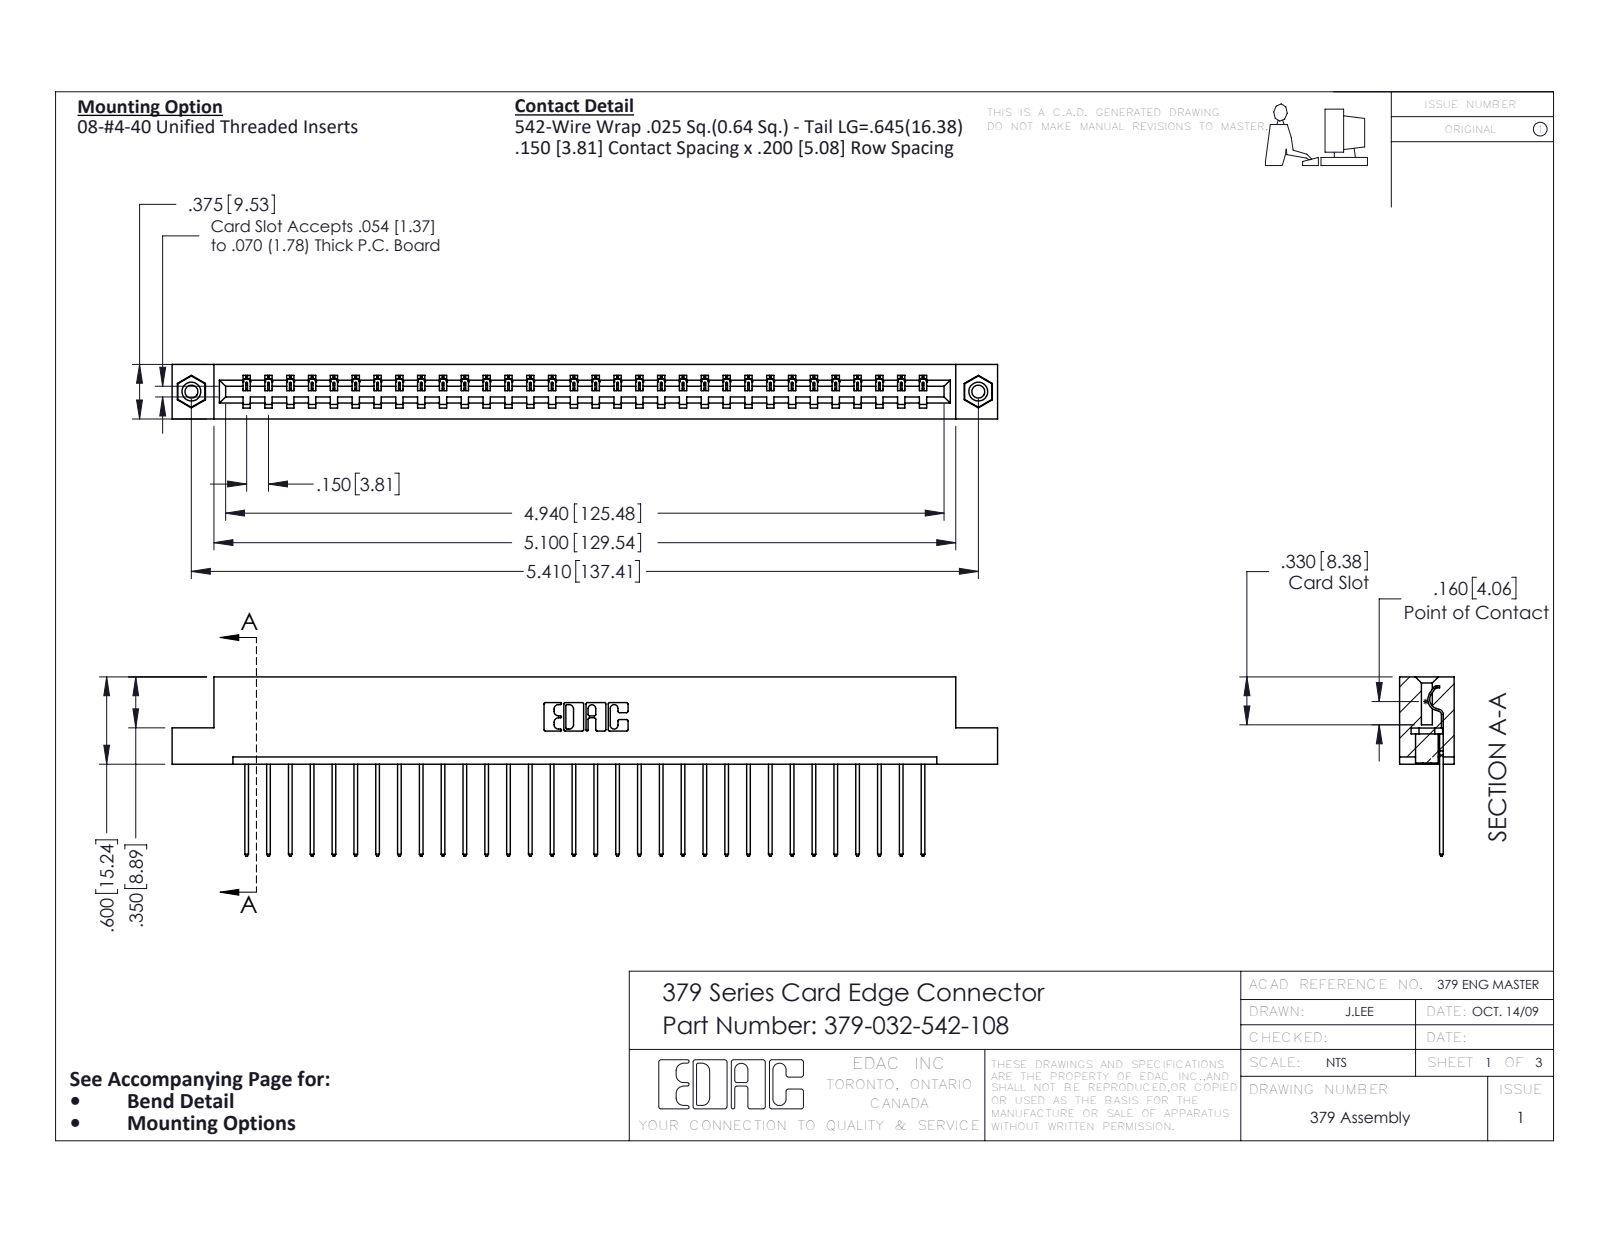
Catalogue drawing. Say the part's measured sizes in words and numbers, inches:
The part is named "345-292-001_345-293-142; 379-032-542-108; 345-250-001_345-250-003-102; 379 Part_Flush - .156 Dia - TI". Its 3-D file was written by "SolidWorks 2016 (CONFIG_CONTROL_DESIGN)". It is 35 solids with 2030 faces: 1446 planar, 568 cylindrical and 16 other. Overall it measures 5.675 by 1.232 by 0.375 inches. Its volume is 0.921 cubic inches and its surface area 24.63 square inches. Round holes: 2 of diameter 0.089, 2 of diameter 0.125, 2 of diameter 0.156. Round bosses or shafts: 2 of diameter 0.155. Partial cylindrical surfaces (rounded edges, fillets, slot ends): 64 of radius 0.006, 64 of radius 0.01, 22 of radius 0.01, 6 of radius 0.007, 6 of radius 0.031, 3 of radius 0.026, 1 of radius 0.014, 1 of radius 0.022. The main face-to-face distances are 0.3, 0.075, 0.375, 0.225, 0.275, 0.1, 0.025, 0.2, 0.6, 0.55. The hole center spacings are 5.41.
